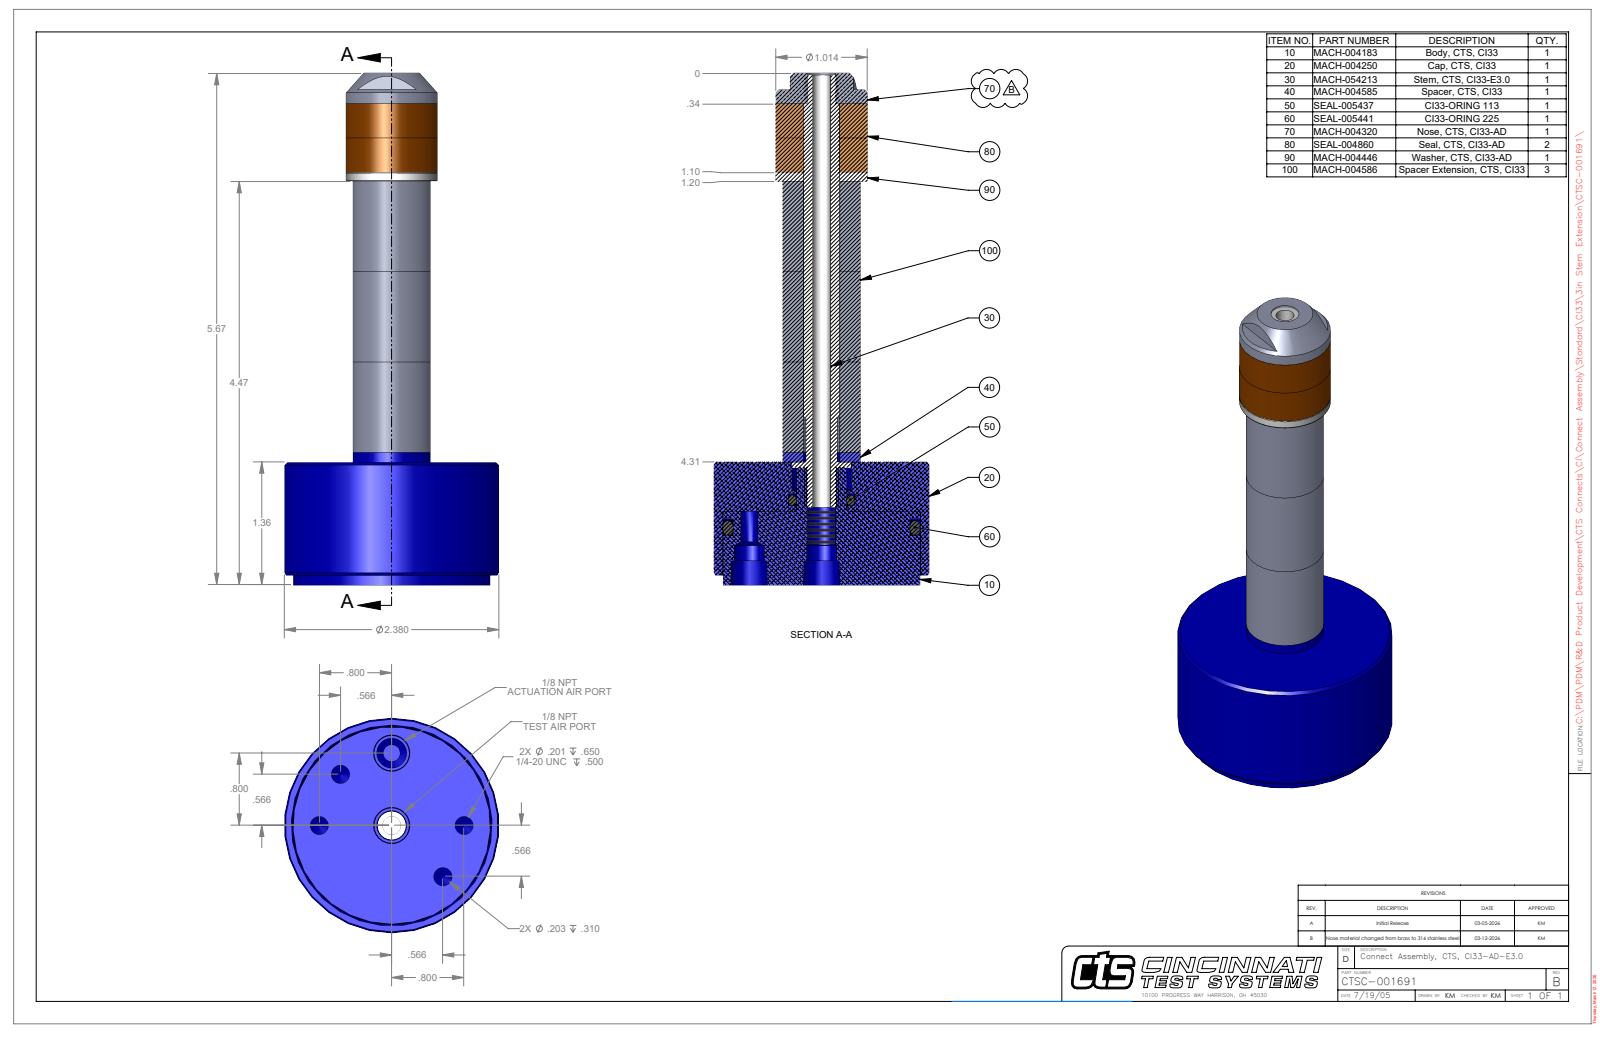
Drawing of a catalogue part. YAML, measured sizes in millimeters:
part_name: "CTSC-001691"
step_written_by: "SolidWorks 2023 (AUTOMOTIVE_DESIGN)"
units: millimeters
bodies: {solids: 9, faces: 82, planar: 39, cylindrical: 30, other: 13}
overall_size: [143.94, 60.45, 60.45]
volume: 137107
surface_area: 35764
round_holes:
  - {diameter: 5.11, count: 2}
  - {diameter: 5.16, count: 2}
  - {diameter: 5.16, count: 1}
  - {diameter: 7.94, count: 1}
  - {diameter: 8.43, count: 1}
  - {diameter: 9.91, count: 1}
  - {diameter: 10.24, count: 1}
  - {diameter: 16.74, count: 1}
  - {diameter: 55.58, count: 1}
round_bosses_or_shafts:
  - {diameter: 60.45, count: 1}
  - {diameter: 55.32, count: 1}
  - {diameter: 25.76, count: 1}
  - {diameter: 21.79, count: 1}
  - {diameter: 16.51, count: 1}
  - {diameter: 9.93, count: 1}
  - {diameter: 9.53, count: 1}
face_to_face_distances: [34.54, 25.4, 50.8, 135.31, 100.77, 125.65, 91.11, 9.66, 116, 81.46]
hole_center_spacings: [20.32, 15.55, 37.55, 40.64]
